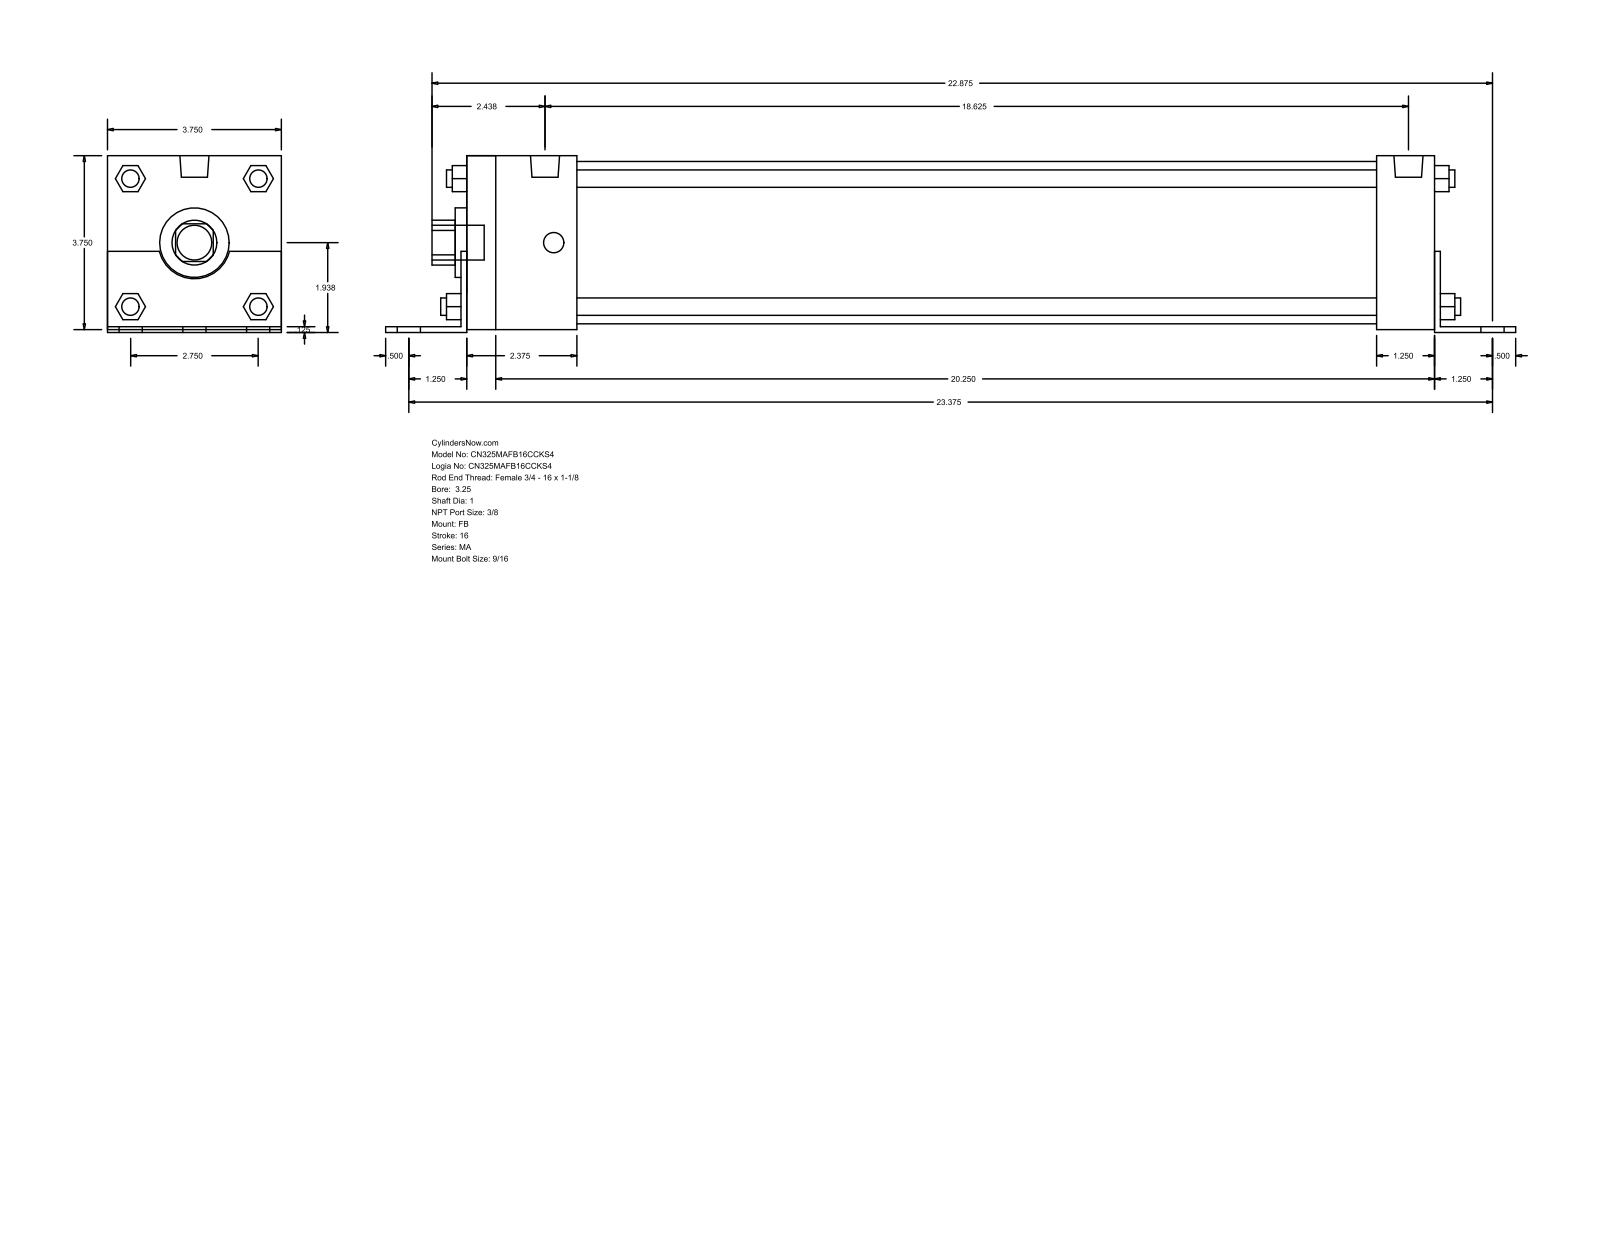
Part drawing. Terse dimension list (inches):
name: MA_FB__0325_1
written by: GSSL Pune (CONFIG_CONTROL_DESIGN)
unit: in
bodies: 0 solids, 140 faces (105 planar, 35 cylindrical, 0 other)
size: 24.375 × 3.813 × 3.75
holes: 1× ⌀1, 1× ⌀1.5, 1× ⌀3.5
bosses: 6× ⌀0.563, 4× ⌀0.437, 4× ⌀0.375, 2× ⌀0.627, 1× ⌀0.75
rounds: 1× R0.484, 1× R0.78
face distances: 3.75, 0.125, 0.063, 3.812, 0.062, 3.687, 0.125, 20.875, 21.125, 21
